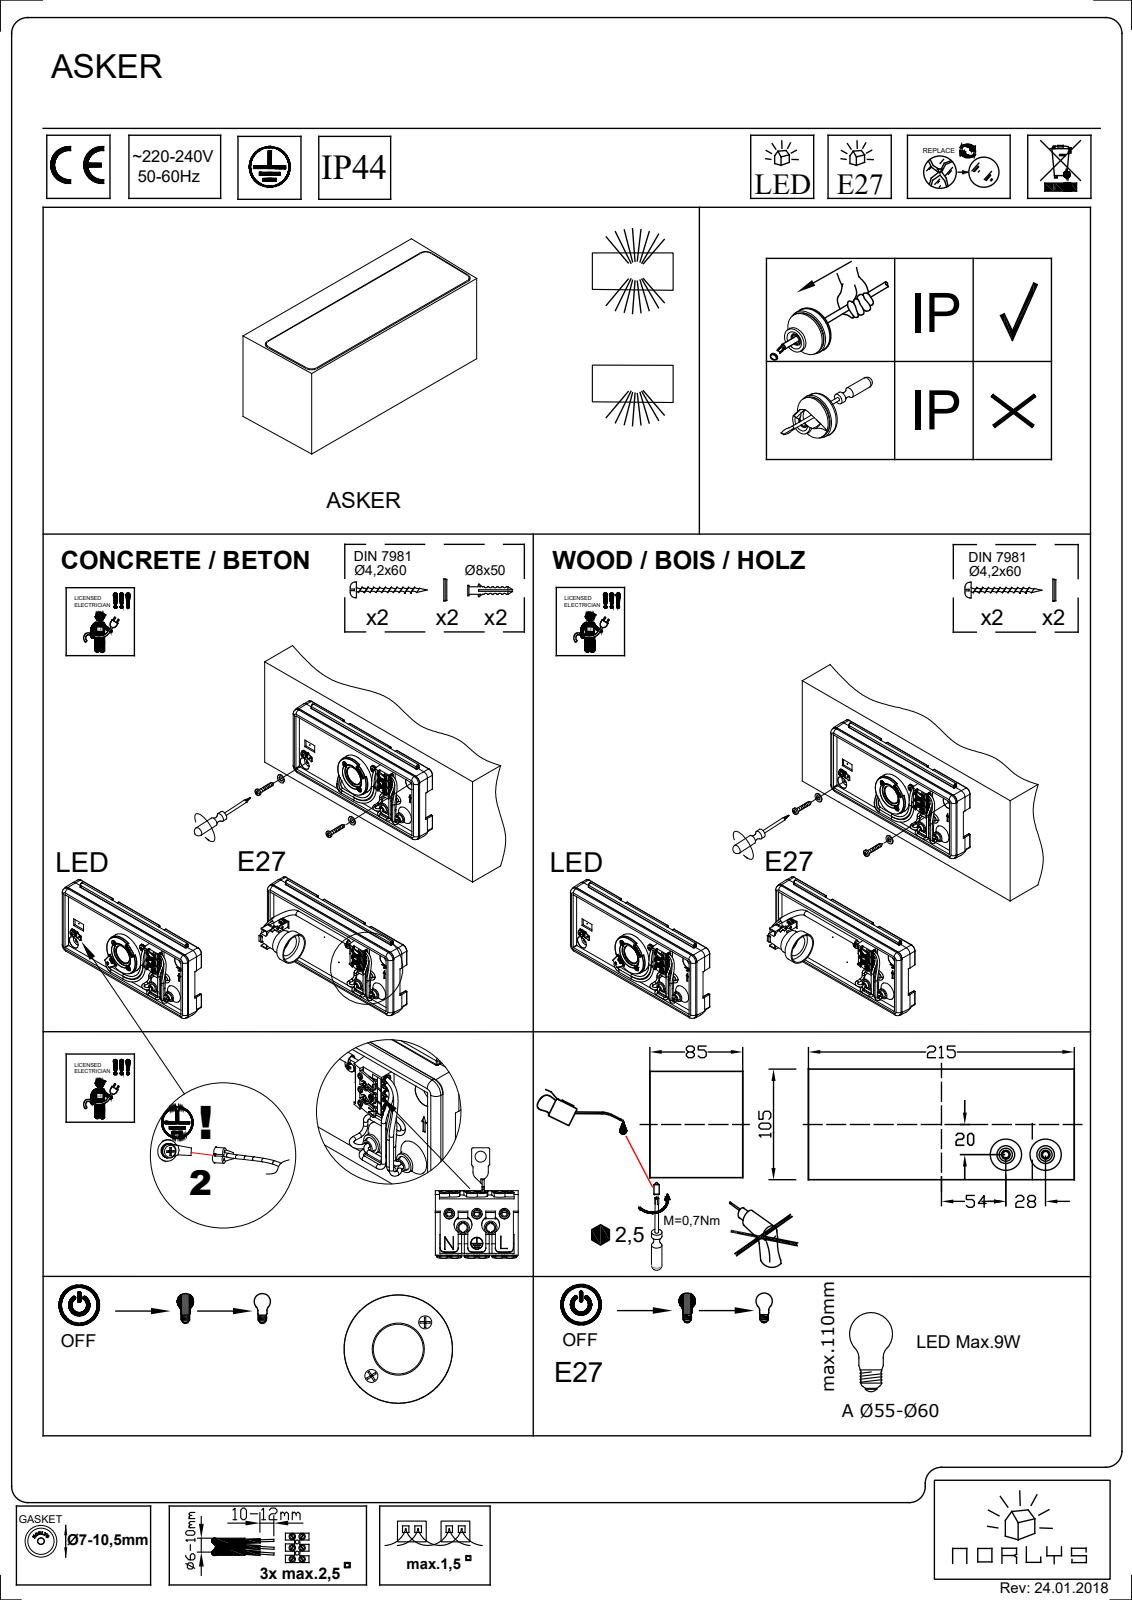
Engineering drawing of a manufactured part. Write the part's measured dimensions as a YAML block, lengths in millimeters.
step_written_by: "ACIS (automotive_design)"
units: millimeters
bodies: {solids: 2, faces: 35, planar: 9, cylindrical: 16, other: 10}
overall_size: [130, 26, 26]
volume: 49612
surface_area: 16057
round_holes:
  - {diameter: 20.48, count: 1}
round_bosses_or_shafts:
  - {diameter: 26, count: 1}
  - {diameter: 20, count: 1}
partial_cylinders:
  - {radius: 1.44, count: 1}
  - {radius: 2.37, count: 1}
  - {radius: 3.26, count: 1}
  - {radius: 9.99, count: 1}
face_to_face_distances: [45, 130, 85, 0.92, 95.24, 50.24, 34.76]
